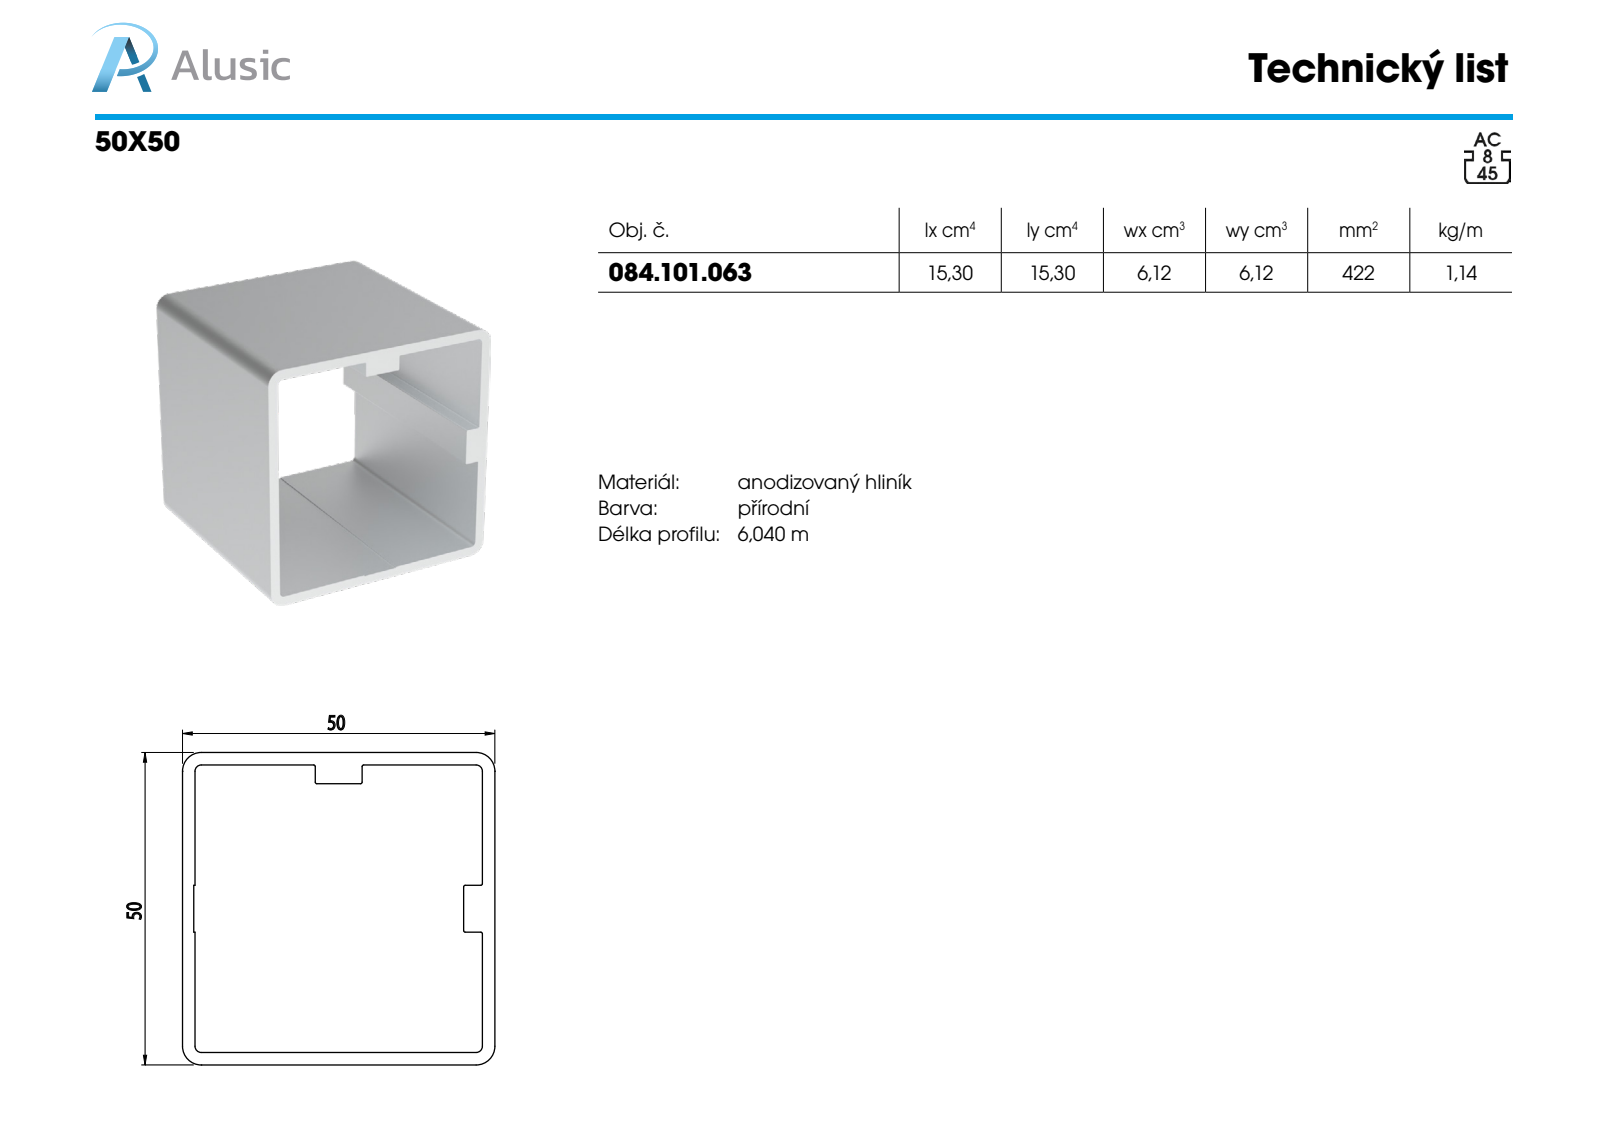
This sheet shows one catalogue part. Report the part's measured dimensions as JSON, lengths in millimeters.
{"part_name": "084.101.063", "step_written_by": "SolidWorks 2018 (AUTOMOTIVE_DESIGN)", "units": "millimeters", "bodies": {"solids": 1, "faces": 38, "planar": 22, "cylindrical": 16, "other": 0}, "overall_size": [100, 50, 50], "volume_mm3": 42063, "surface_area_mm2": 39709, "partial_cylinders_radius": [[0.25, 8], [1, 4], [3, 4]], "face_to_face_distances": [48, 2, 50, 46, 45, 43, 3, 5, 21.25, 28.75]}
